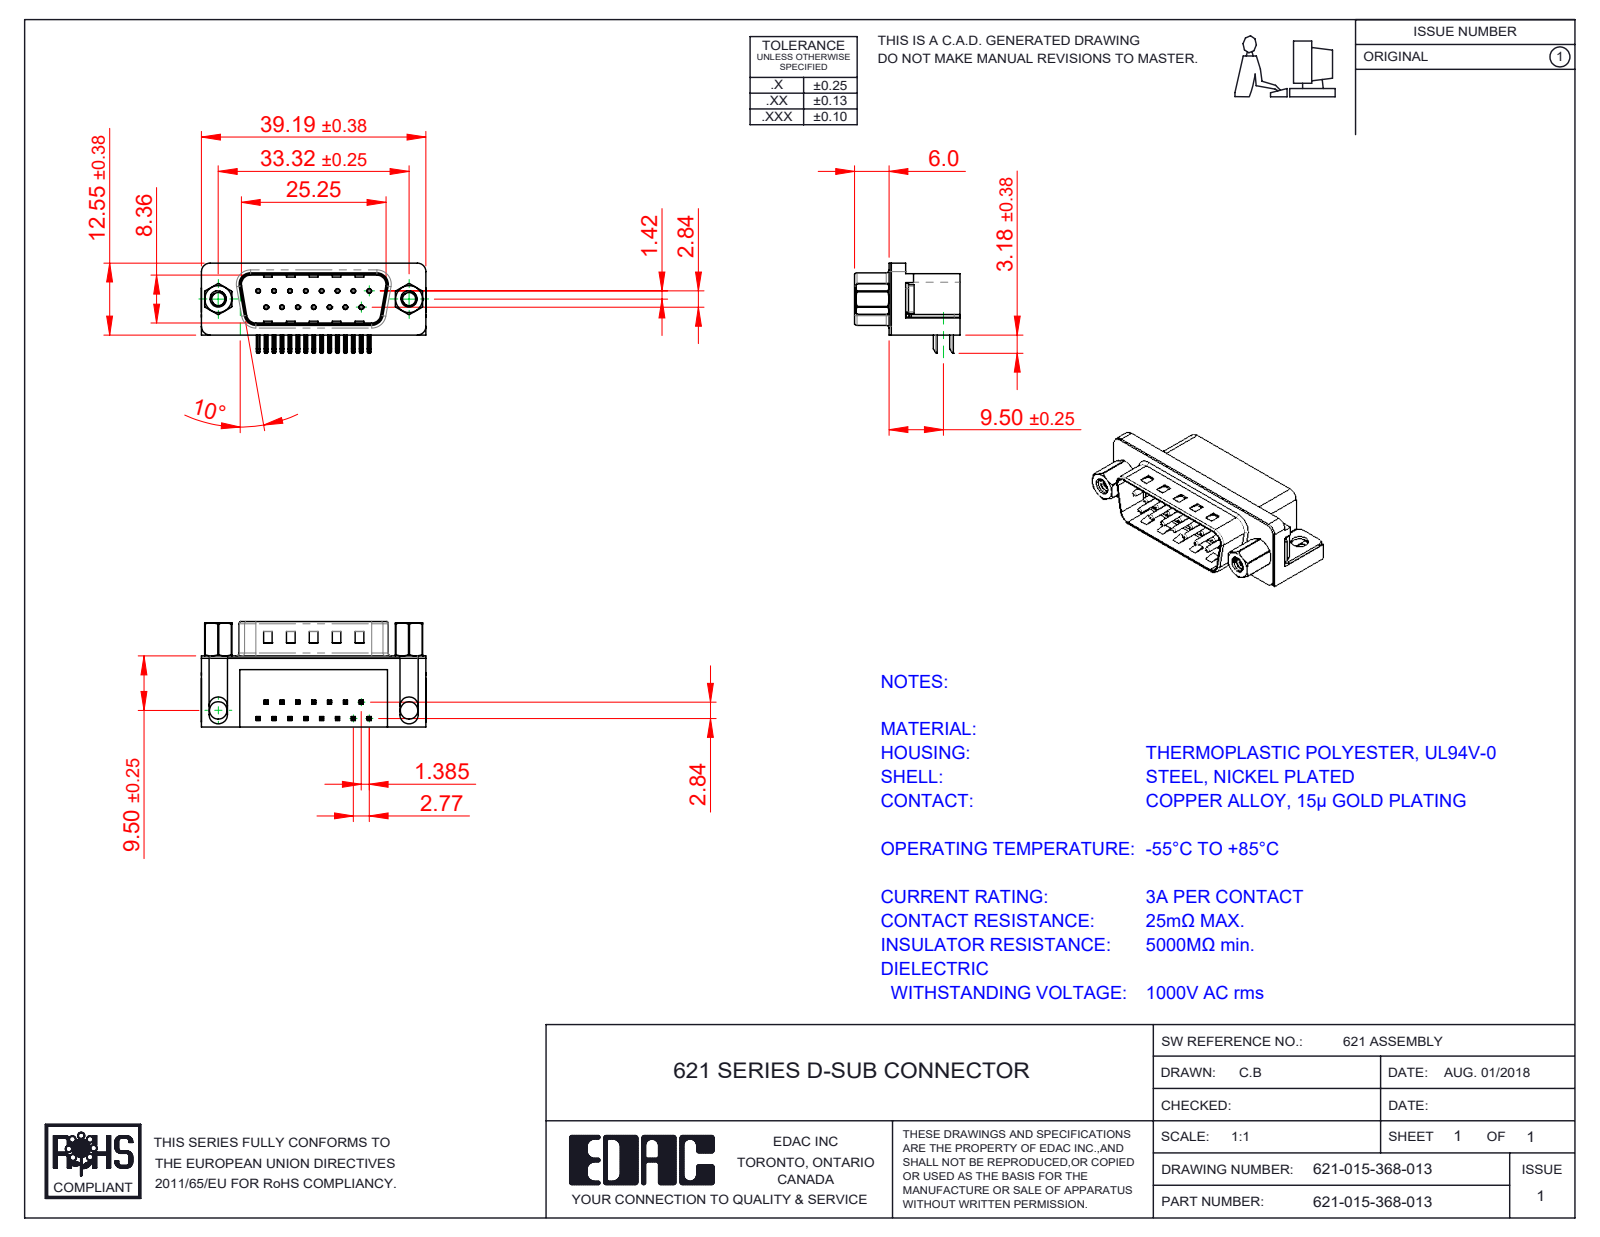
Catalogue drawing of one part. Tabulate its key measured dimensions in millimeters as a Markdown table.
| quantity | value |
| --- | --- |
| part name | 621 Shell_15 Socket; 621 4-40 Hex Standoff 5; 621 4-40 Threaded Rivet; 621 Housing_15 Socket (+4 more) |
| STEP written by | SolidWorks 2016 (CONFIG_CONTROL_DESIGN) |
| units | millimeters |
| bodies | 23 solids, 1601 faces (913 planar, 517 cylindrical, 171 other) |
| overall size | 39.22 × 18.4 × 15.73 |
| volume | 4 626 mm³ |
| surface area | 6 120 mm² |
| round holes (diameter × count) | 0.35 × 15, 0.8 × 15, 2.26 × 2, 2.29 × 2, 3.05 × 2, 4 × 2, 4.8 × 2, 5 × 2 |
| round bosses / shafts (diameter × count) | 0.75 × 15, 4.9 × 2, 4.75 × 2, 3.9 × 2, 2.79 × 2 |
| partial cylindrical surfaces (radius × count) | 0.25 × 68, 0.12 × 30, 1 × 16, 0.5 × 9, 1.6 × 8, 1.5 × 6, 0.9 × 4, 2 × 4 |
| main face-to-face distances | 0.4, 12, 10.35, 12.4, 2.1, 10.46, 1.7, 10.86, 8.76, 9.5 |
| hole center spacings | 3.16, 2.77, 5.54, 8.31, 11.08, 5.03, 5.04, 7.48 |
